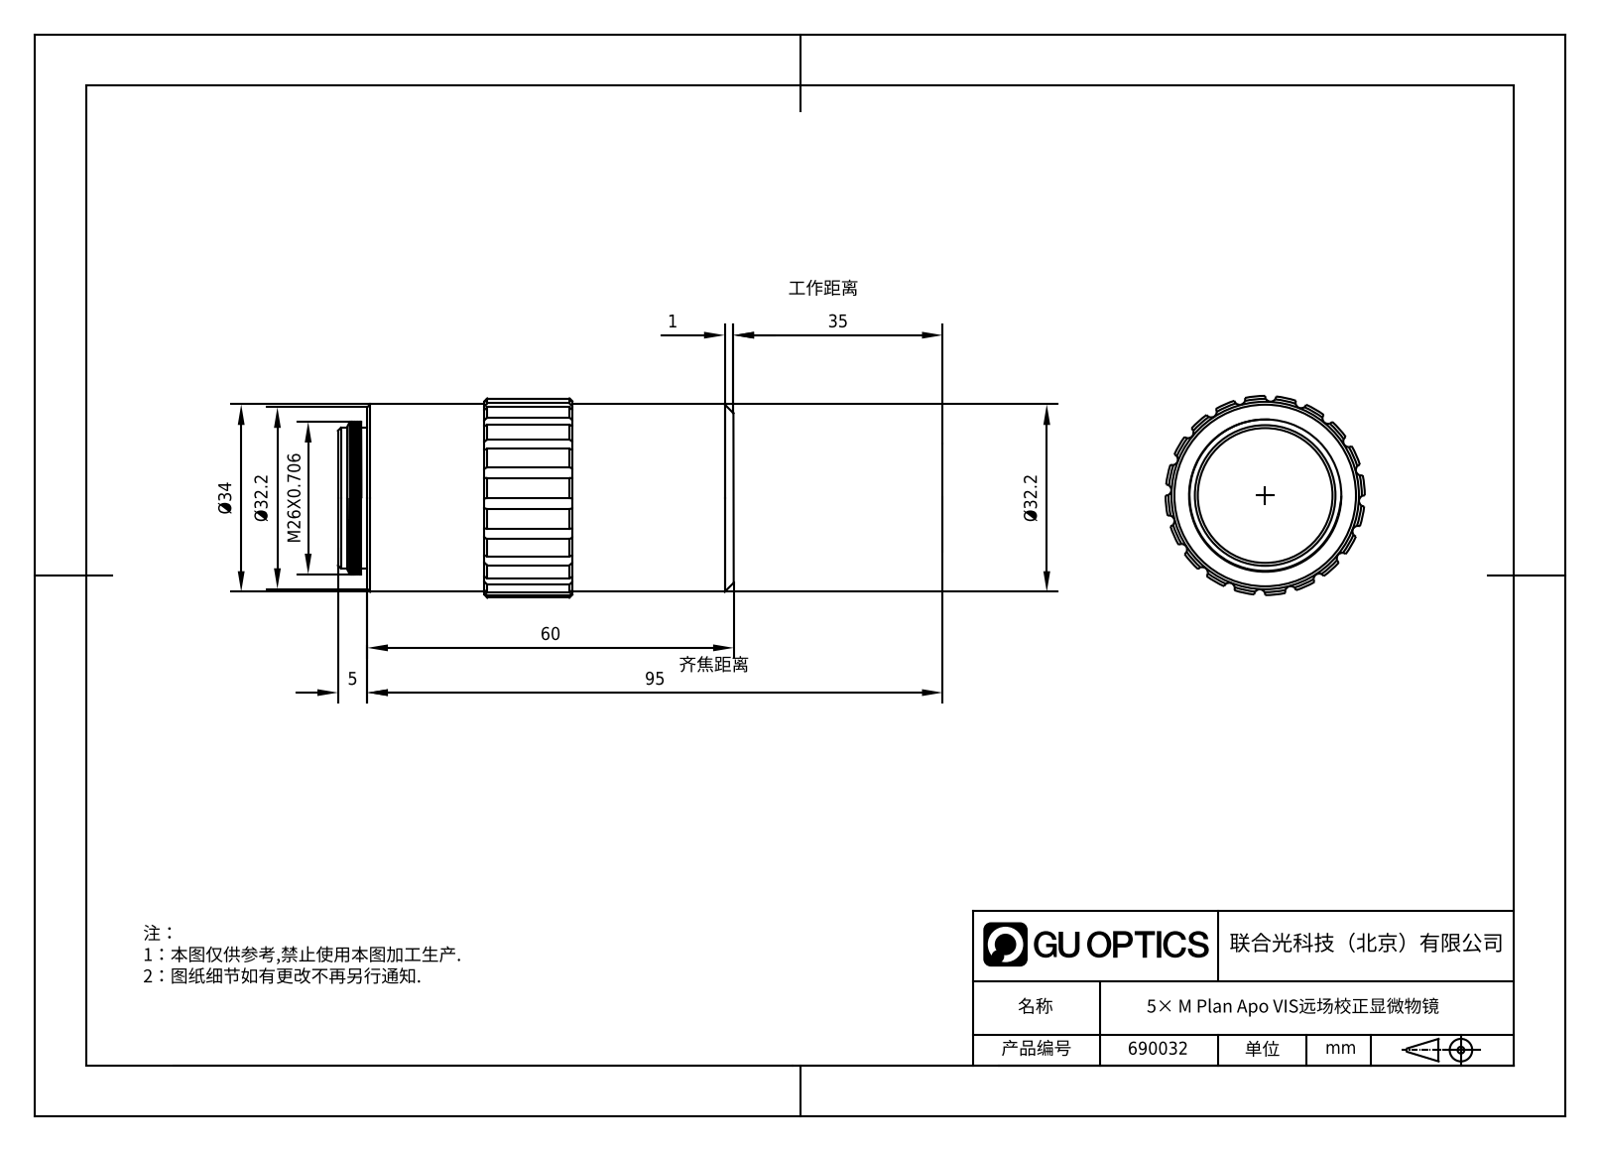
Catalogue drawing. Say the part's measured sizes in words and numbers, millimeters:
The part is named "690032". Its 3-D file was written by "SolidWorks 2020 (CONFIG_CONTROL_DESIGN)". It is 4 solids with 312 faces: 146 planar, 76 cylindrical and 90 other. Overall it measures 66.65 by 33.97 by 33.97 millimeters. Its volume is 50 946 cubic millimeters and its surface area 13 600 square millimeters. Round holes: 1 of diameter 17. Round bosses or shafts: 1 of diameter 32.2, 1 of diameter 32, 1 of diameter 26, 1 of diameter 24. Partial cylindrical surfaces (rounded edges, fillets, slot ends): 16 of radius 0.71, 1 of radius 16, 1 of radius 17. The main face-to-face distances are 66, 1.44, 64.56, 61, 59.56, 5, 10, 8.56, 51, 56.
